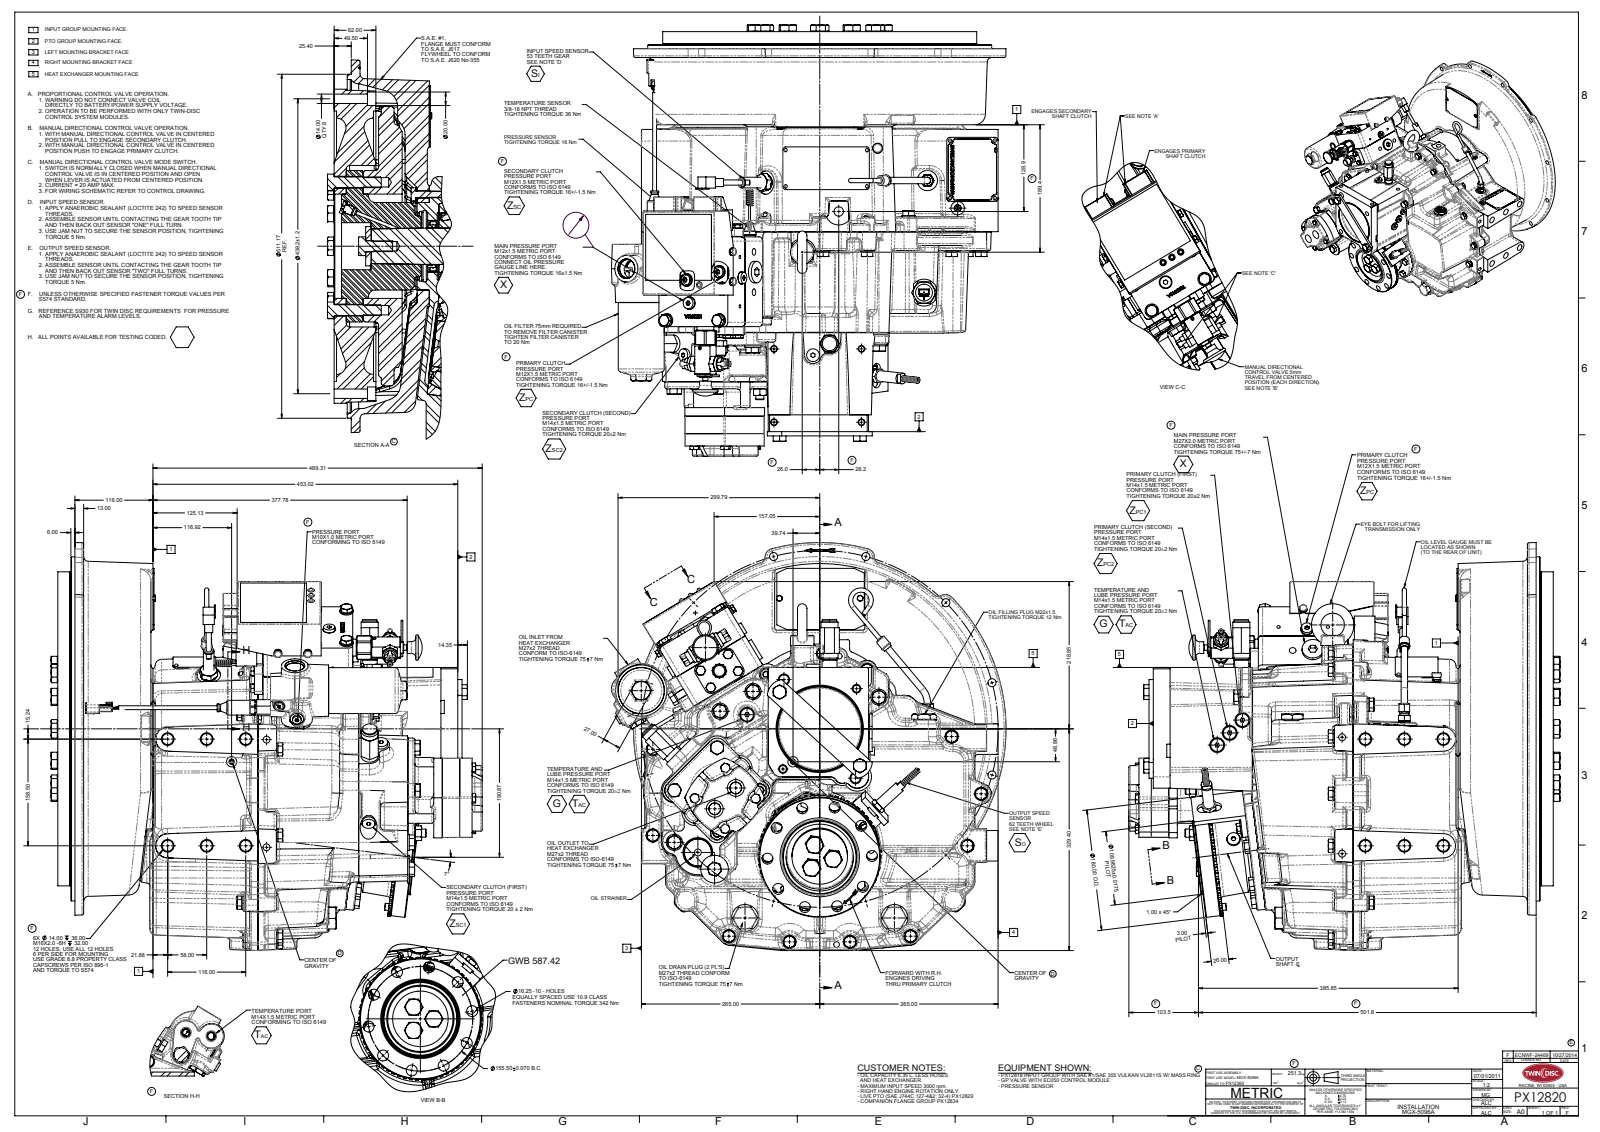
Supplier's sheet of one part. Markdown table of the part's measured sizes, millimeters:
| quantity | value |
| --- | --- |
| part name | PX12820 |
| STEP written by | SolidWorks 2010 (AUTOMOTIVE_DESIGN) |
| units | millimeters |
| bodies | 0 solids, 5150 faces (1455 planar, 1531 cylindrical, 2164 other) |
| overall size | 640.71 × 606.29 × 586.41 |
| round holes (diameter × count) | 12 × 12, 8.5 × 10, 14 × 10, 16.25 × 10, 10 × 6, 17 × 6, 18.82 × 6, 10.2 × 5, 4.8 × 4, 19 × 3, 25 × 3, 12.8 × 2 |
| round bosses / shafts (diameter × count) | 19.85 × 19, 24 × 15, 19 × 8, 17 × 5, 2.54 × 5, 20 × 4, 13 × 4, 11 × 4 |
| partial cylindrical surfaces (radius × count) | 3 × 136, 5 × 133, 2.5 × 79, 32 × 77, 4 × 63, 2 × 43, 8 × 25, 10 × 25 |
| main face-to-face distances | 0.5, 149.64, 159.38, 158.88, 138.4, 297.28, 297.78, 447.42, 309.02, 150.14 |
| hole center spacings | 91.4, 147.89, 265.1, 48.05, 459.17, 48.06, 125.8, 125.81 |
